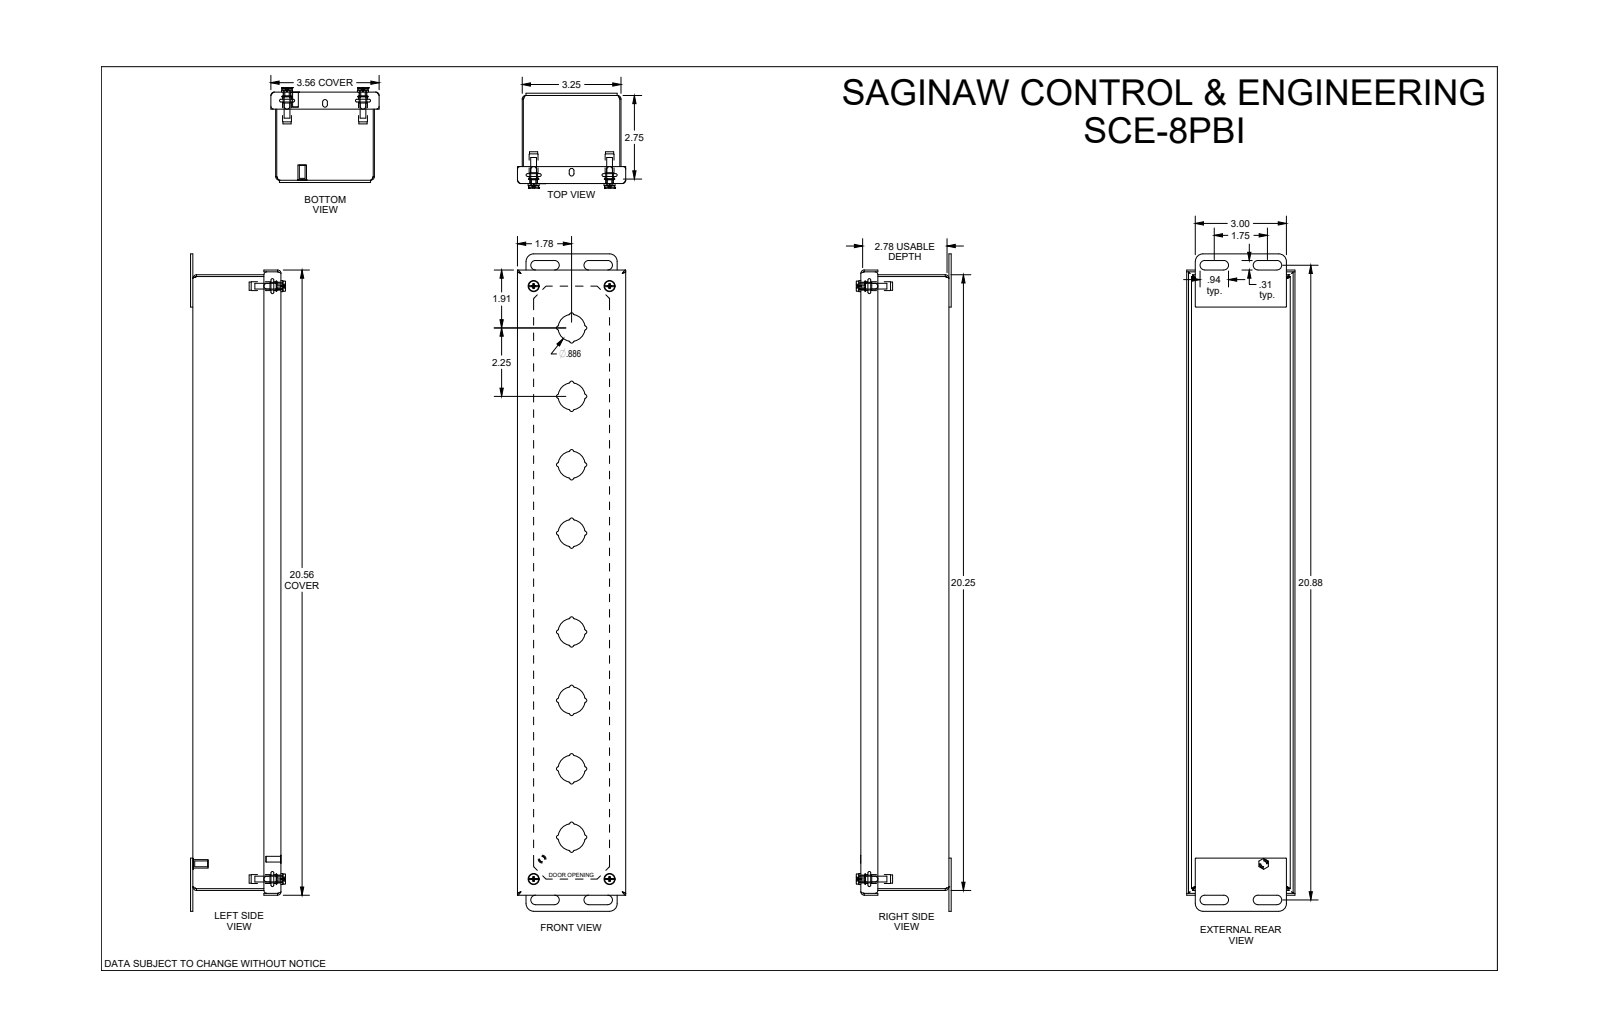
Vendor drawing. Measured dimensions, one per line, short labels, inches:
name: SCE-8PBI
written by: SolidWorks 2021 (AUTOMOTIVE_DESIGN)
unit: in
bodies: 3 solids, 544 faces (153 planar, 307 cylindrical, 84 other)
size: 21.625 × 3.563 × 3.036
volume: 19.69 in³; area: 644 in²
holes: 5× ⌀0.19, 4× ⌀0.22, 4× ⌀0.25, 4× ⌀0.266, 4× ⌀0.317
bosses: 4× ⌀0.362, 4× ⌀0.34, 4× ⌀0.292, 4× ⌀0.27, 4× ⌀0.26, 1× ⌀0.28, 1× ⌀0.256, 1× ⌀0.188
rounds: 64× R0.04, 32× R0.062, 20× R0.06, 8× R0.015, 8× R0.115, 8× R0.156, 8× R0.245, 8× R0.443
face distances: 0.06, 2.838, 3.19, 2.778, 2.898, 3.25, 3.13, 0.156, 3.346, 2.69
hole spacings: 2.5, 19.5, 19.5, 19.659, 19.659, 2.5, 2.5, 0.7
